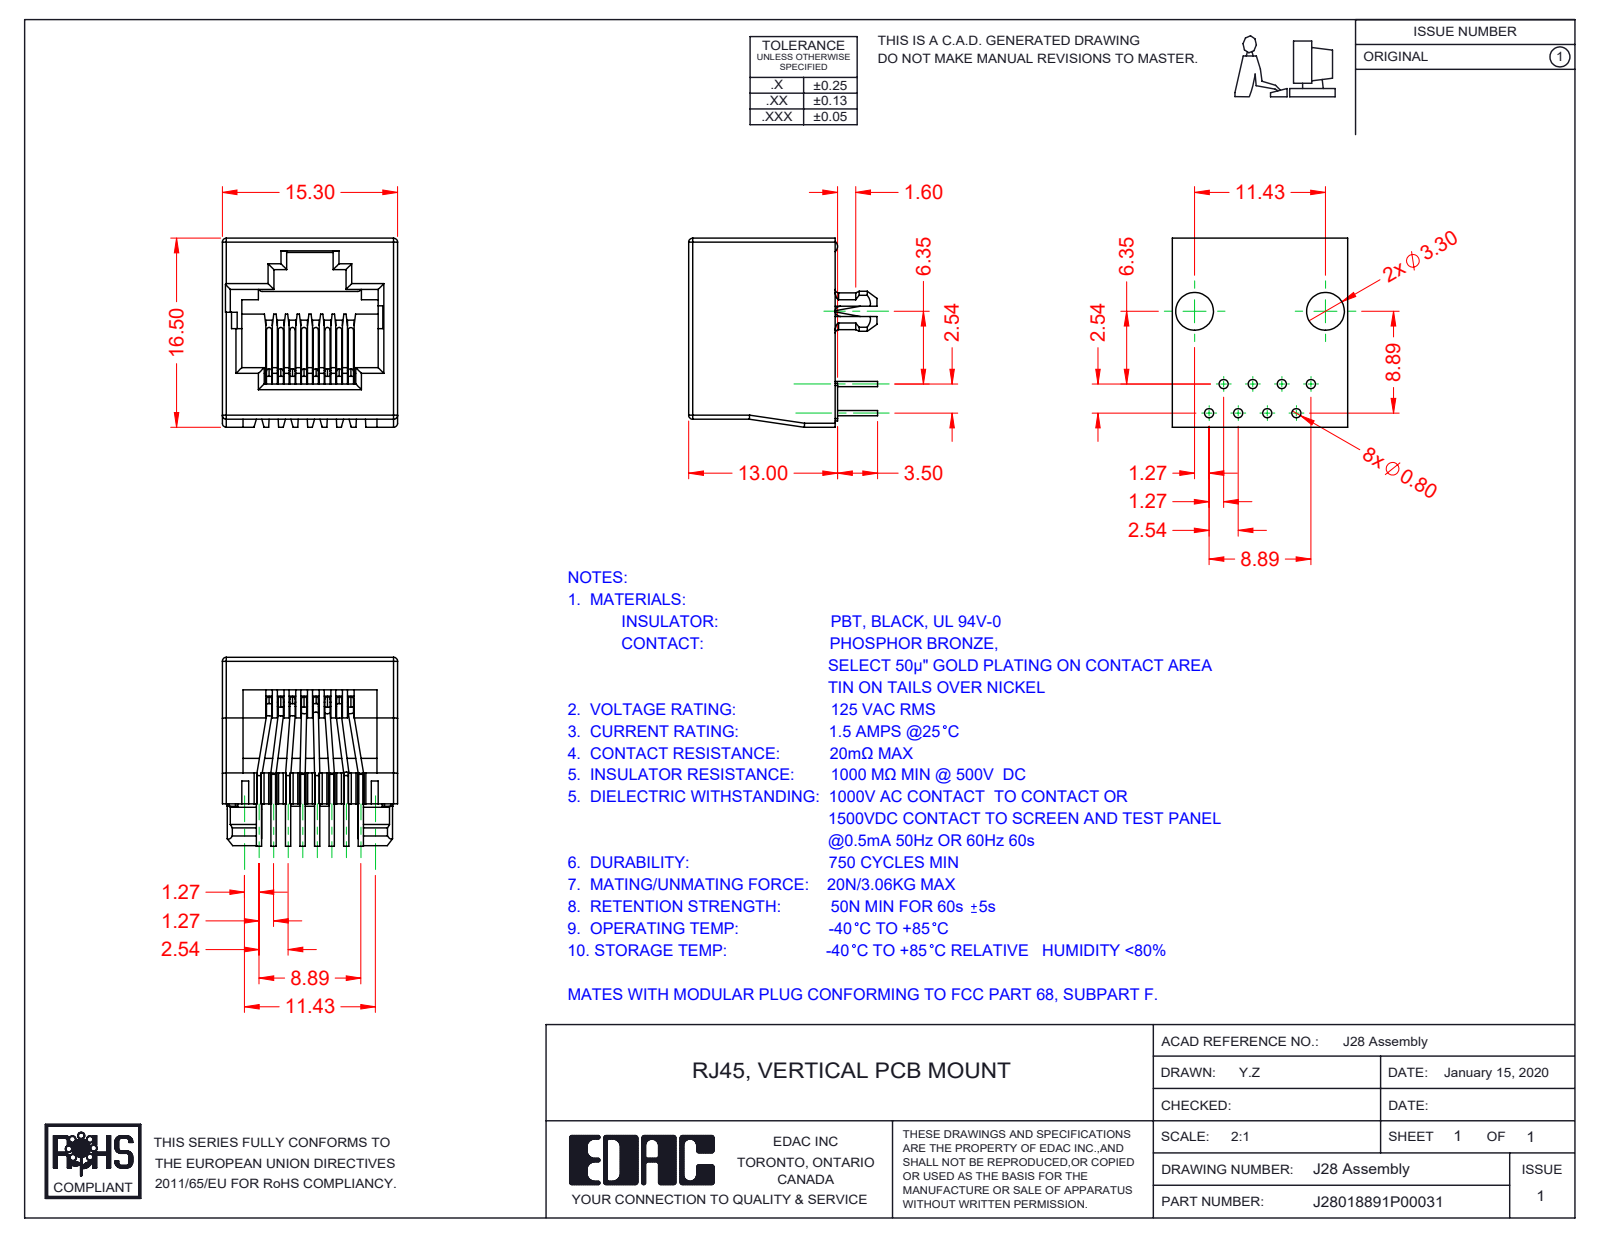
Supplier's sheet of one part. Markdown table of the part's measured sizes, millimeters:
| quantity | value |
| --- | --- |
| part name | 28 Insulator; 28 Contacts; RJ28018891P00031 |
| STEP written by | SolidWorks 2016 (CONFIG_CONTROL_DESIGN) |
| units | millimeters |
| bodies | 9 solids, 580 faces (319 planar, 205 cylindrical, 56 other) |
| overall size | 16.5 × 16.5 × 15.3 |
| volume | 1 535 mm³ |
| surface area | 2 745 mm² |
| round holes (diameter × count) | 1.6 × 2 |
| round bosses / shafts (diameter × count) | 0.46 × 45 |
| partial cylindrical surfaces (radius × count) | 0.5 × 19, 0.1 × 16, 0.35 × 14, 0.25 × 10, 0.2 × 8, 0.23 × 8, 0.45 × 2, 1.6 × 2 |
| main face-to-face distances | 15.3, 1.02, 1.7, 13.6, 1.25, 2.04, 12.81, 3.06, 3.15, 12.15 |
| hole center spacings | 12 |
